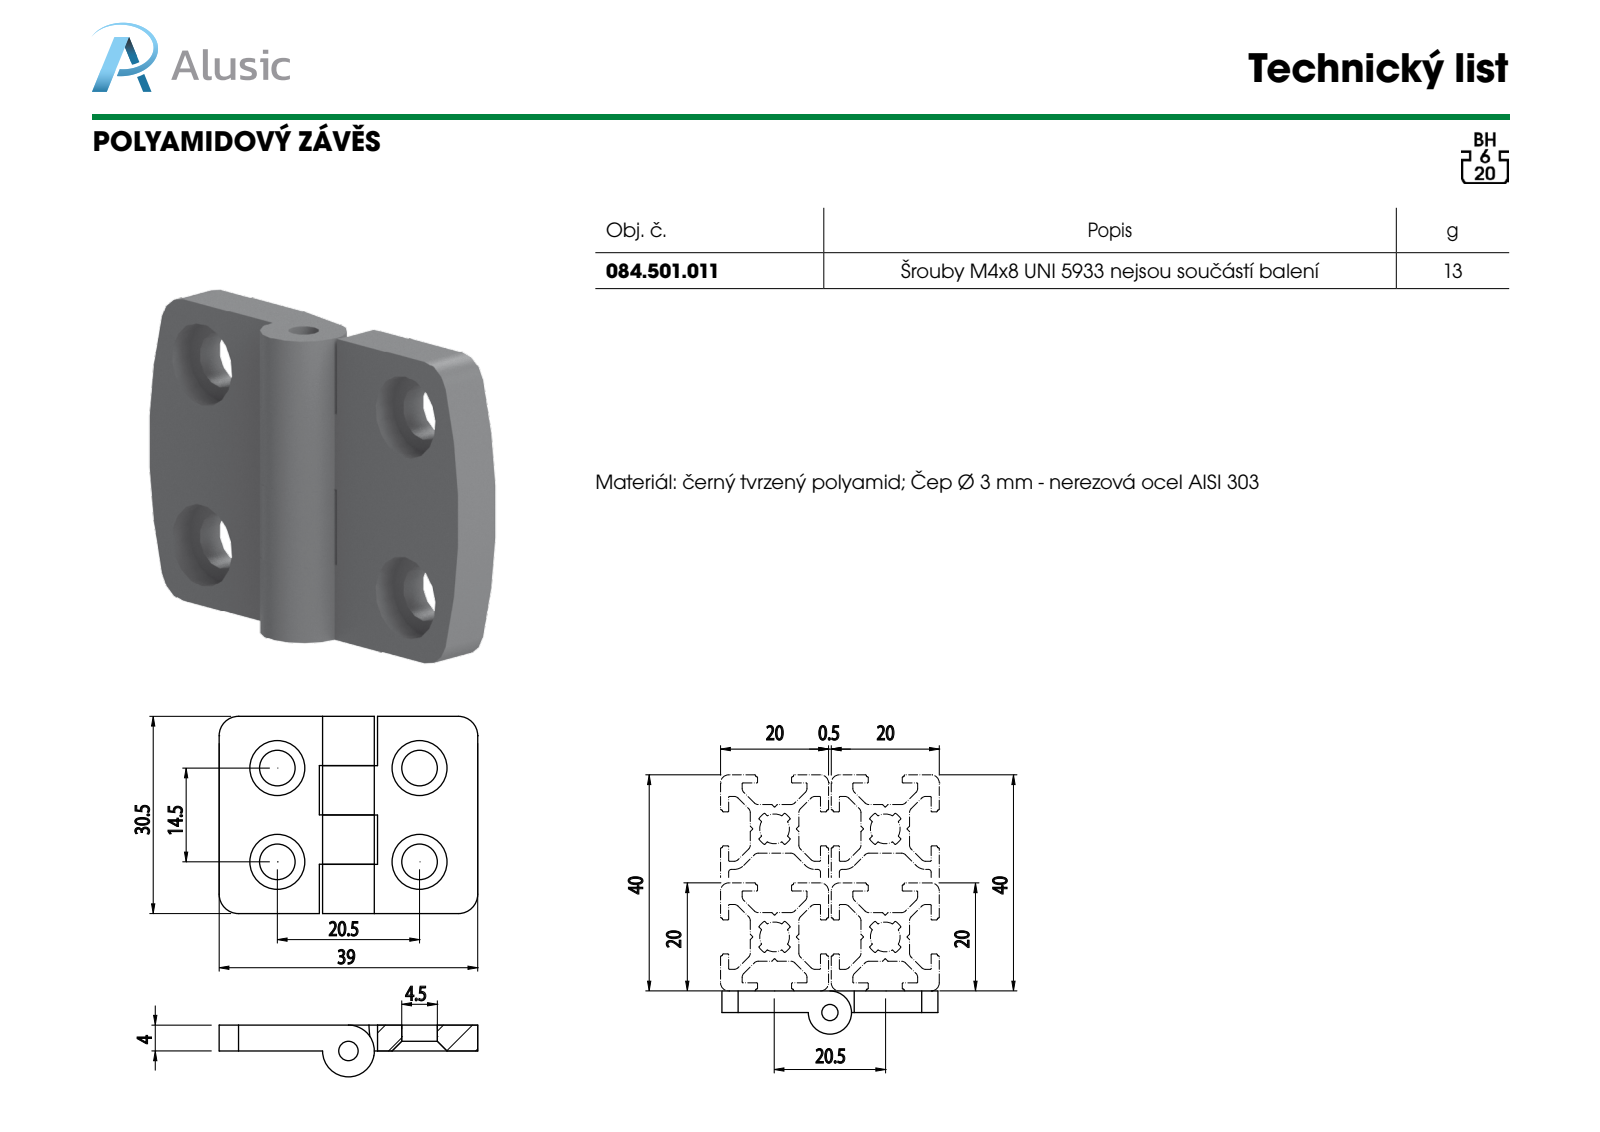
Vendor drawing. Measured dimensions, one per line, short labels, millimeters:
name: 084.501.011
written by: SolidWorks 2012 (CONFIG_CONTROL_DESIGN)
unit: mm
bodies: 1 solid, 26 faces (10 planar, 12 cylindrical, 4 other)
size: 30.5 × 24 × 8
volume: 2 381 mm³; area: 1 955 mm²
holes: 2× ⌀5.5, 1× ⌀3
rounds: 2× R3, 1× R4
face distances: 4, 7.63, 15.26, 15.5, 30.5, 7.61, 15.24, 22.87, 22.89
hole spacings: 14.5
